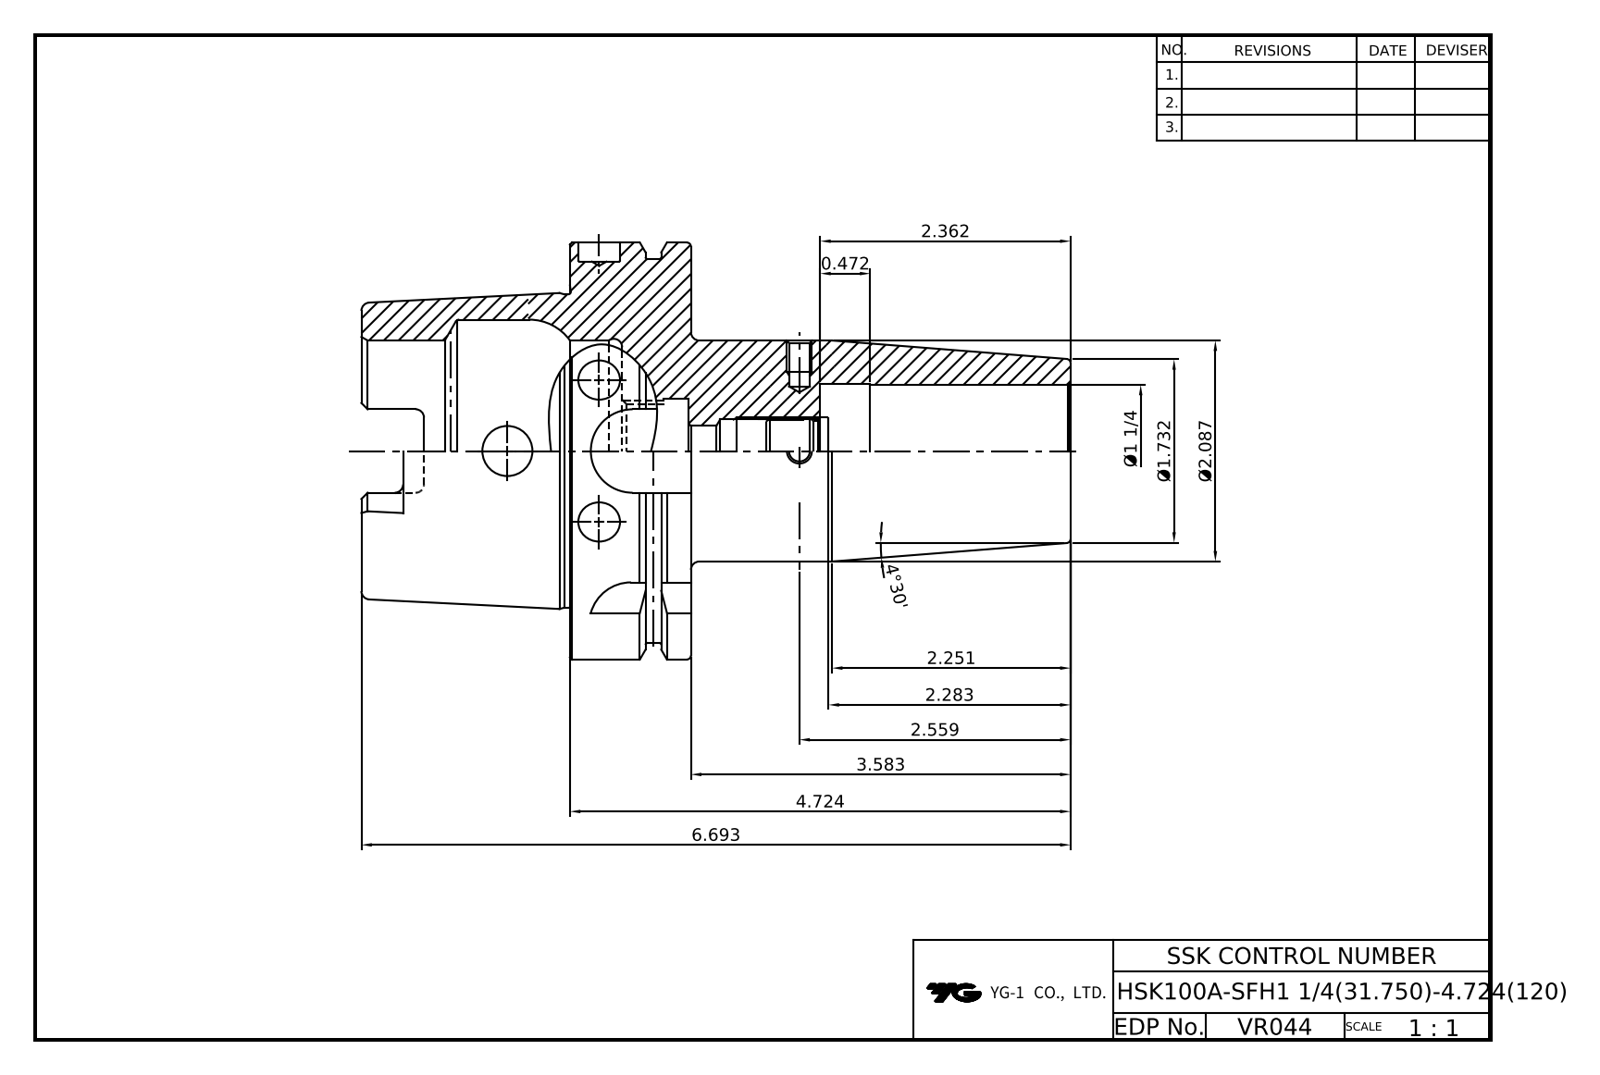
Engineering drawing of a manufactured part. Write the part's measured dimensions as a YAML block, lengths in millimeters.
part_name: "HSK100A-SFH31_75-120"
step_written_by: "CREO PARAMETRIC BY PTC INC, 2018400 (CONFIG_CONTROL_DESIGN)"
units: millimeters
bodies: {solids: 1, faces: 209, planar: 55, cylindrical: 68, other: 86}
overall_size: [170, 100, 100]
volume: 378012
surface_area: 73151
round_holes:
  - {diameter: 5, count: 2}
  - {diameter: 6, count: 2}
  - {diameter: 12, count: 2}
  - {diameter: 10, count: 1}
  - {diameter: 15.1, count: 1}
  - {diameter: 22.5, count: 1}
  - {diameter: 24, count: 1}
  - {diameter: 25, count: 1}
  - {diameter: 31.75, count: 1}
  - {diameter: 32.35, count: 1}
  - {diameter: 53, count: 1}
  - {diameter: 63.96, count: 1}
round_bosses_or_shafts:
  - {diameter: 100, count: 1}
  - {diameter: 92, count: 1}
  - {diameter: 75.16, count: 1}
partial_cylinders:
  - {radius: 2, count: 6}
  - {radius: 4.88, count: 4}
  - {radius: 10, count: 4}
face_to_face_distances: [29, 12.5, 16.5, 60, 62.5, 50, 79, 47.5, 10, 110]
hole_center_spacings: [48, 70]
